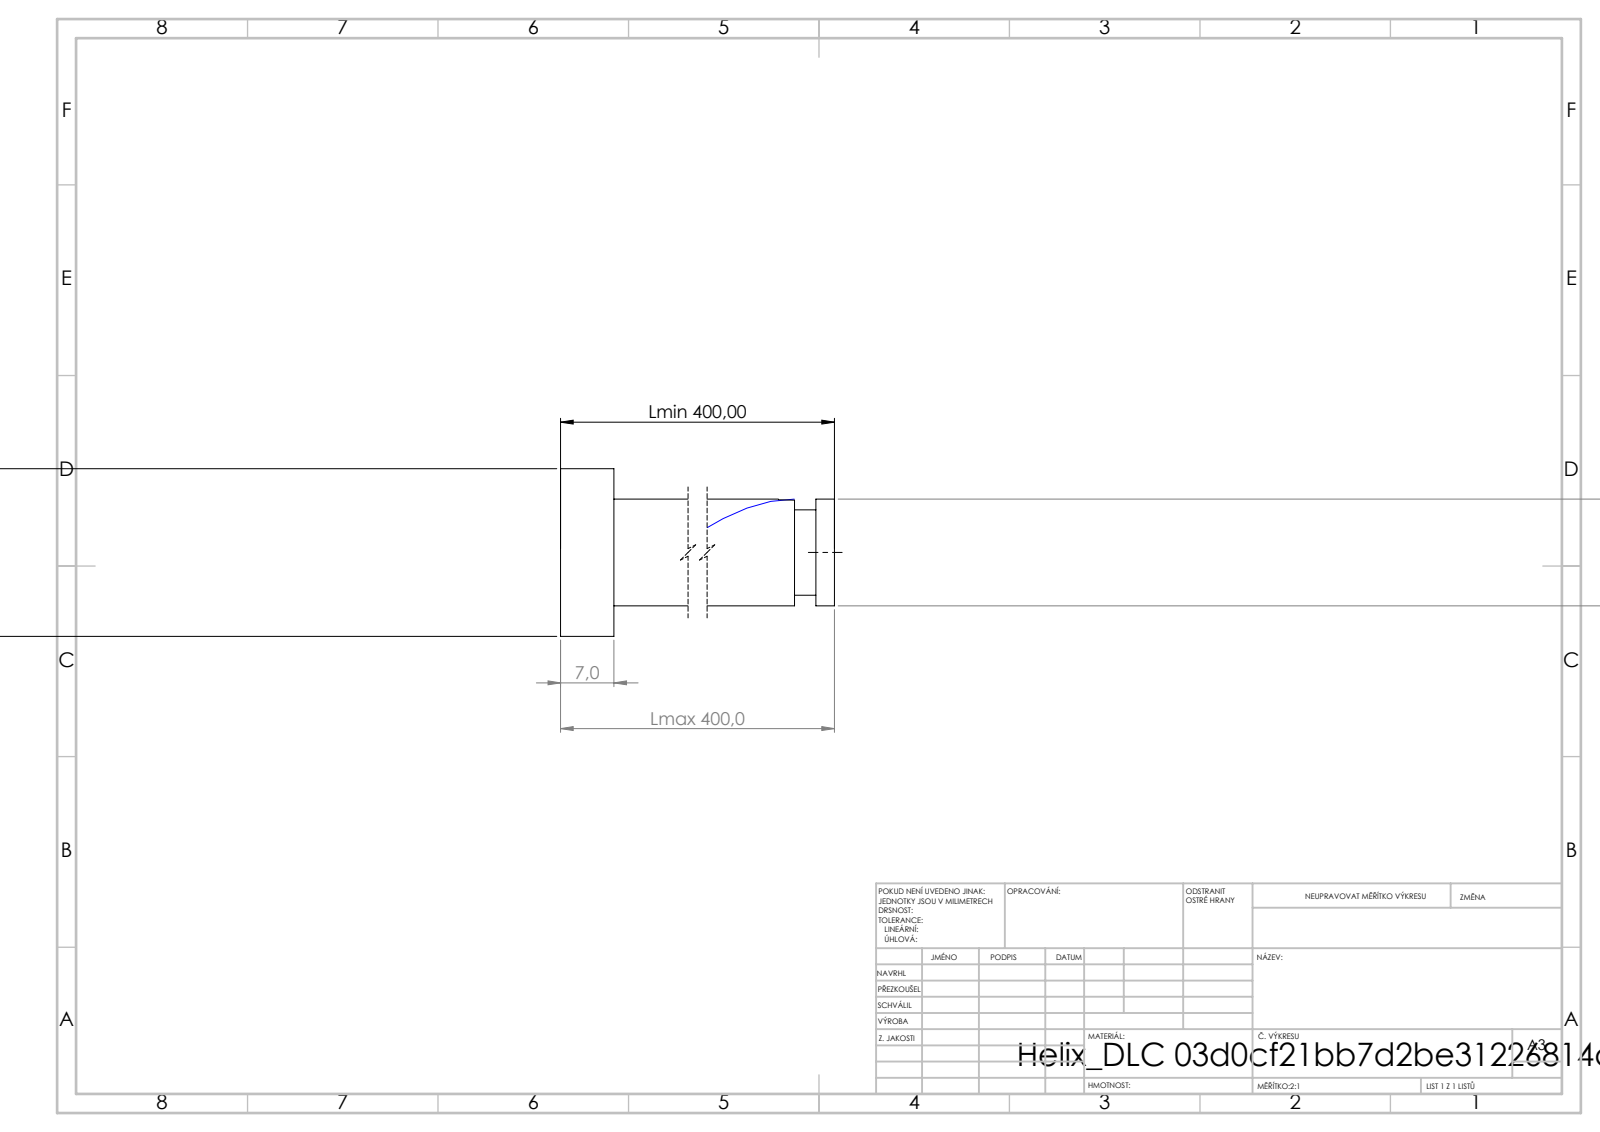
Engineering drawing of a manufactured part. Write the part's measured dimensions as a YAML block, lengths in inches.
step_written_by: "SolidWorks 2019 (CONFIG_CONTROL_DESIGN)"
units: inches
bodies: {solids: 1, faces: 21, planar: 6, cylindrical: 14, other: 1}
overall_size: [15.748, 0.866, 0.866]
volume: 3.809
surface_area: 29.38
round_bosses_or_shafts:
  - {diameter: 0.866, count: 1}
  - {diameter: 0.551, count: 1}
  - {diameter: 0.441, count: 1}
face_to_face_distances: [0.276, 15.748, 15.472, 15.652, 15.377, 0.096, 15.542, 15.267, 0.11, 0.206]
